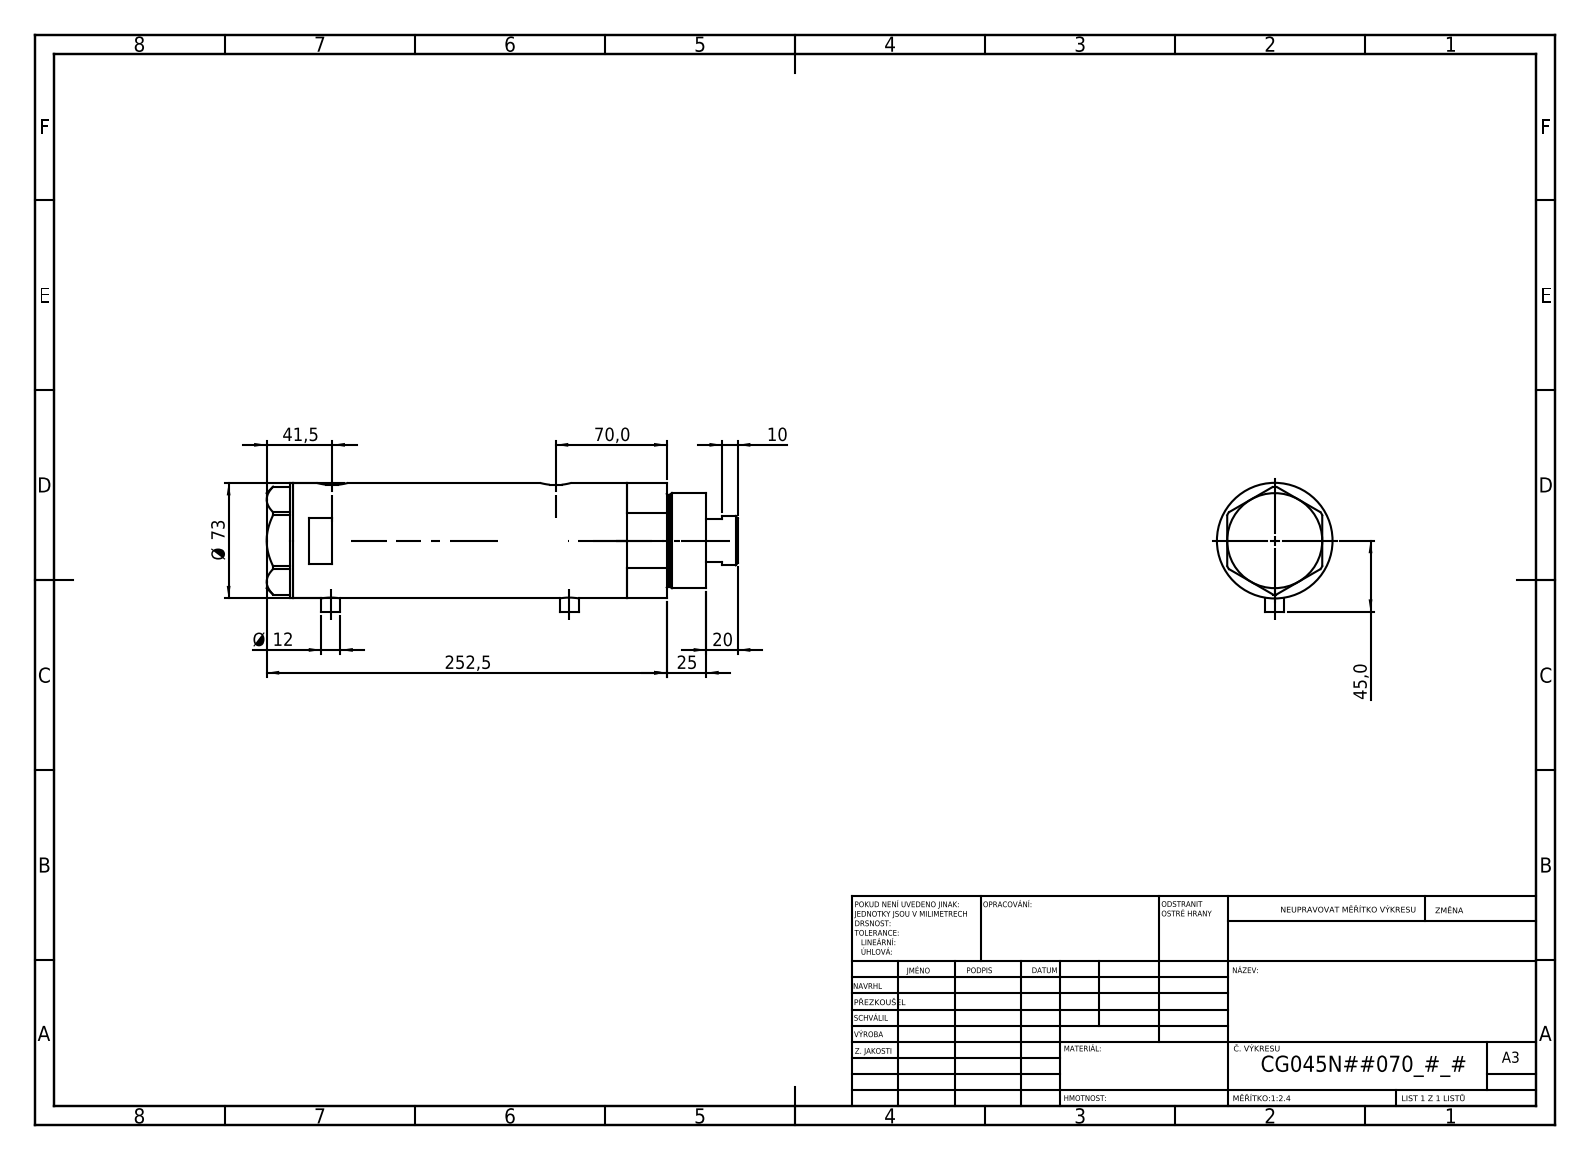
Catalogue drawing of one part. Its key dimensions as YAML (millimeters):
part_name: "V270CG_BACK; V270CG_FRONT; V270CG_VC; V270CG_MIDDLE"
step_written_by: "SolidWorks 2019 (CONFIG_CONTROL_DESIGN)"
units: millimeters
bodies: {solids: 4, faces: 120, planar: 49, cylindrical: 51, other: 20}
overall_size: [297.5, 81.5, 73]
volume: 1059000
surface_area: 171178
round_holes:
  - {diameter: 12.5, count: 2}
  - {diameter: 13.16, count: 2}
  - {diameter: 10.5, count: 1}
  - {diameter: 32, count: 1}
  - {diameter: 33.5, count: 1}
  - {diameter: 45, count: 1}
  - {diameter: 48, count: 1}
  - {diameter: 64, count: 1}
round_bosses_or_shafts:
  - {diameter: 12, count: 2}
  - {diameter: 73, count: 1}
  - {diameter: 60, count: 1}
  - {diameter: 58, count: 1}
  - {diameter: 31, count: 1}
partial_cylinders:
  - {radius: 10, count: 2}
face_to_face_distances: [140, 166, 26, 16.5, 42.5, 182.5, 70, 2, 261, 277.5]
hole_center_spacings: [1, 8.5, 141, 142, 149.5, 150.5]
